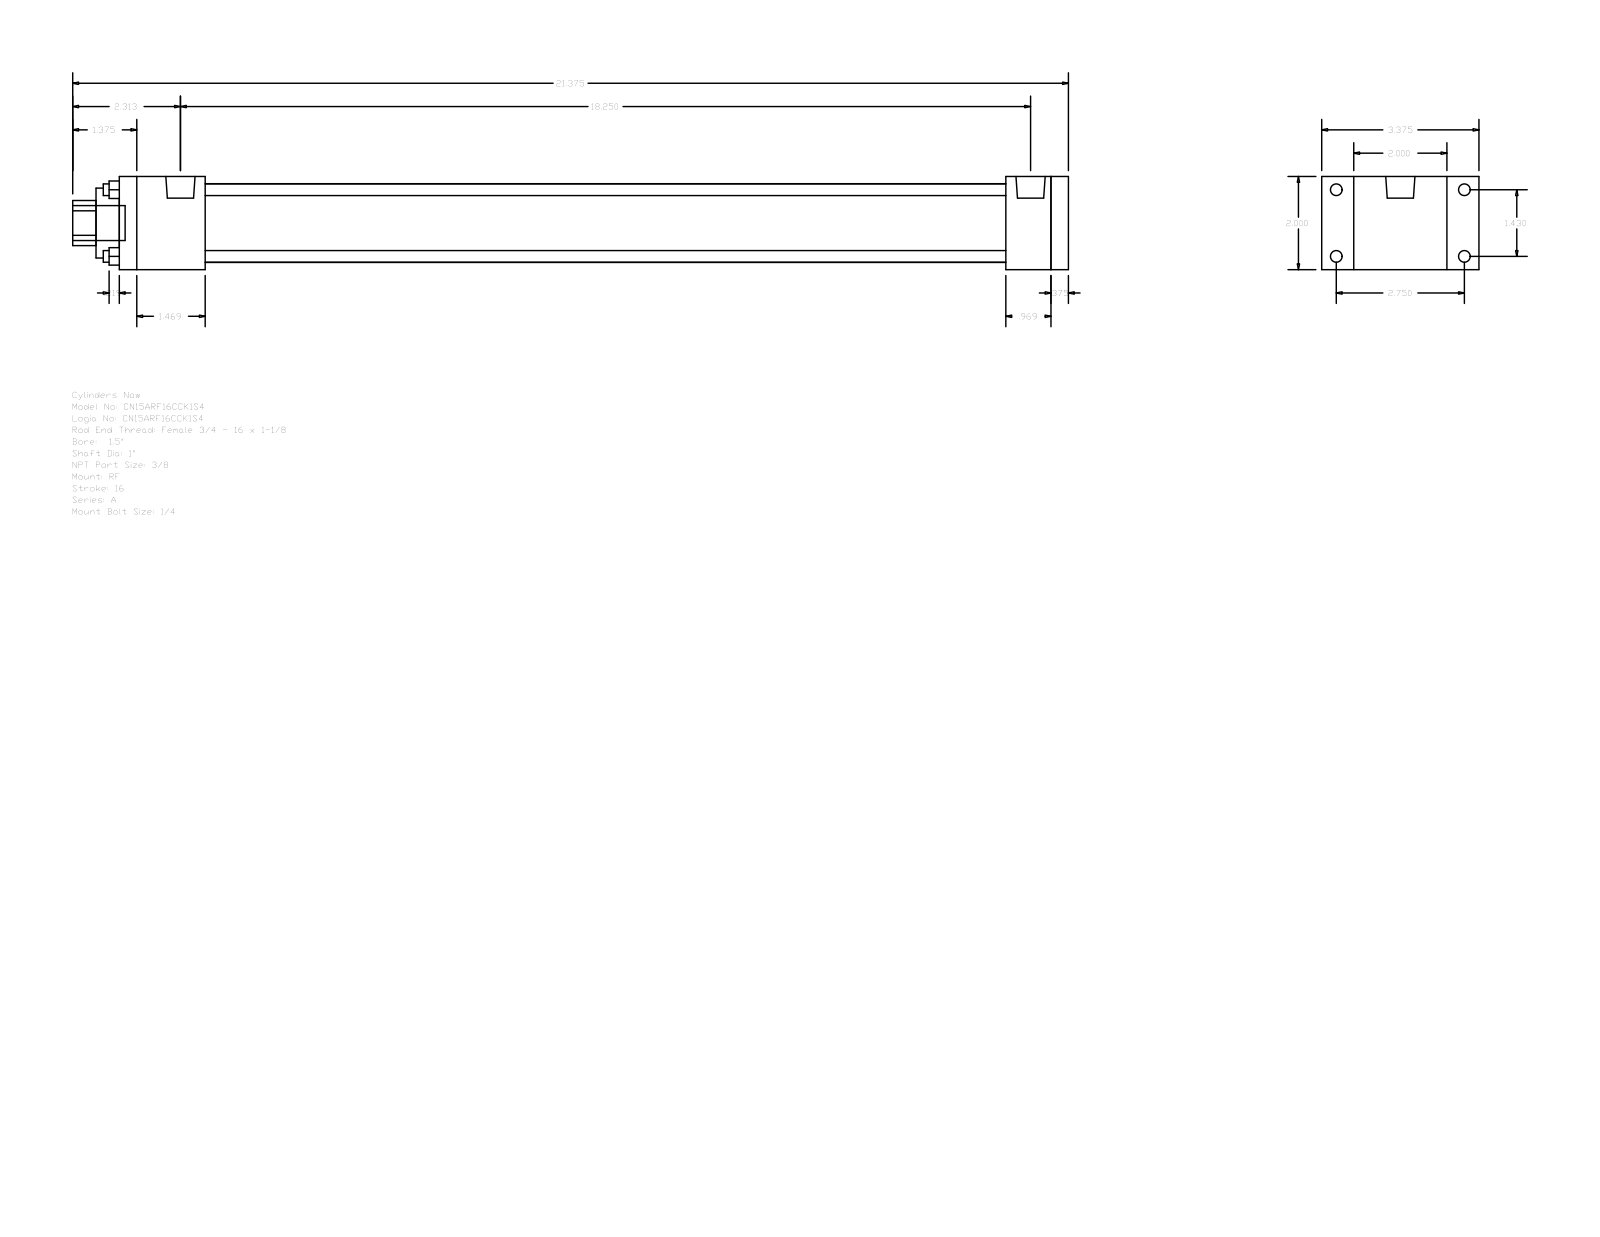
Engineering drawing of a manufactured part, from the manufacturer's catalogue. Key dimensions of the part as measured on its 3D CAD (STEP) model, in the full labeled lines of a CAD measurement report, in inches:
Part name (STEP PRODUCT): A_RF__0150_1
STEP written by: GSSL Pune (CONFIG_CONTROL_DESIGN)
Units: inches
Bodies: 0 solids, 92 faces (64 planar, 28 cylindrical, 0 other)
Overall size (bounding box): 21.375 × 3.375 × 2
Round holes (diameter × count): ⌀0.25 ×4, ⌀1 ×1, ⌀1.5 ×1, ⌀1.69 ×1
Round bosses / shafts (diameter × count): ⌀0.25 ×4, ⌀0.219 ×4, ⌀0.627 ×2, ⌀0.75 ×1
Partial cylindrical surfaces — rounded edges, fillets, slot ends (radius × count): R0.484 ×1
Main face-to-face distances: 2, 0.375, 20, 20.375, 19.031, 0.969, 1.344, 1.844, 17.187, 18.156
Hole centre spacings: 1.011, 1.43, 2.022
